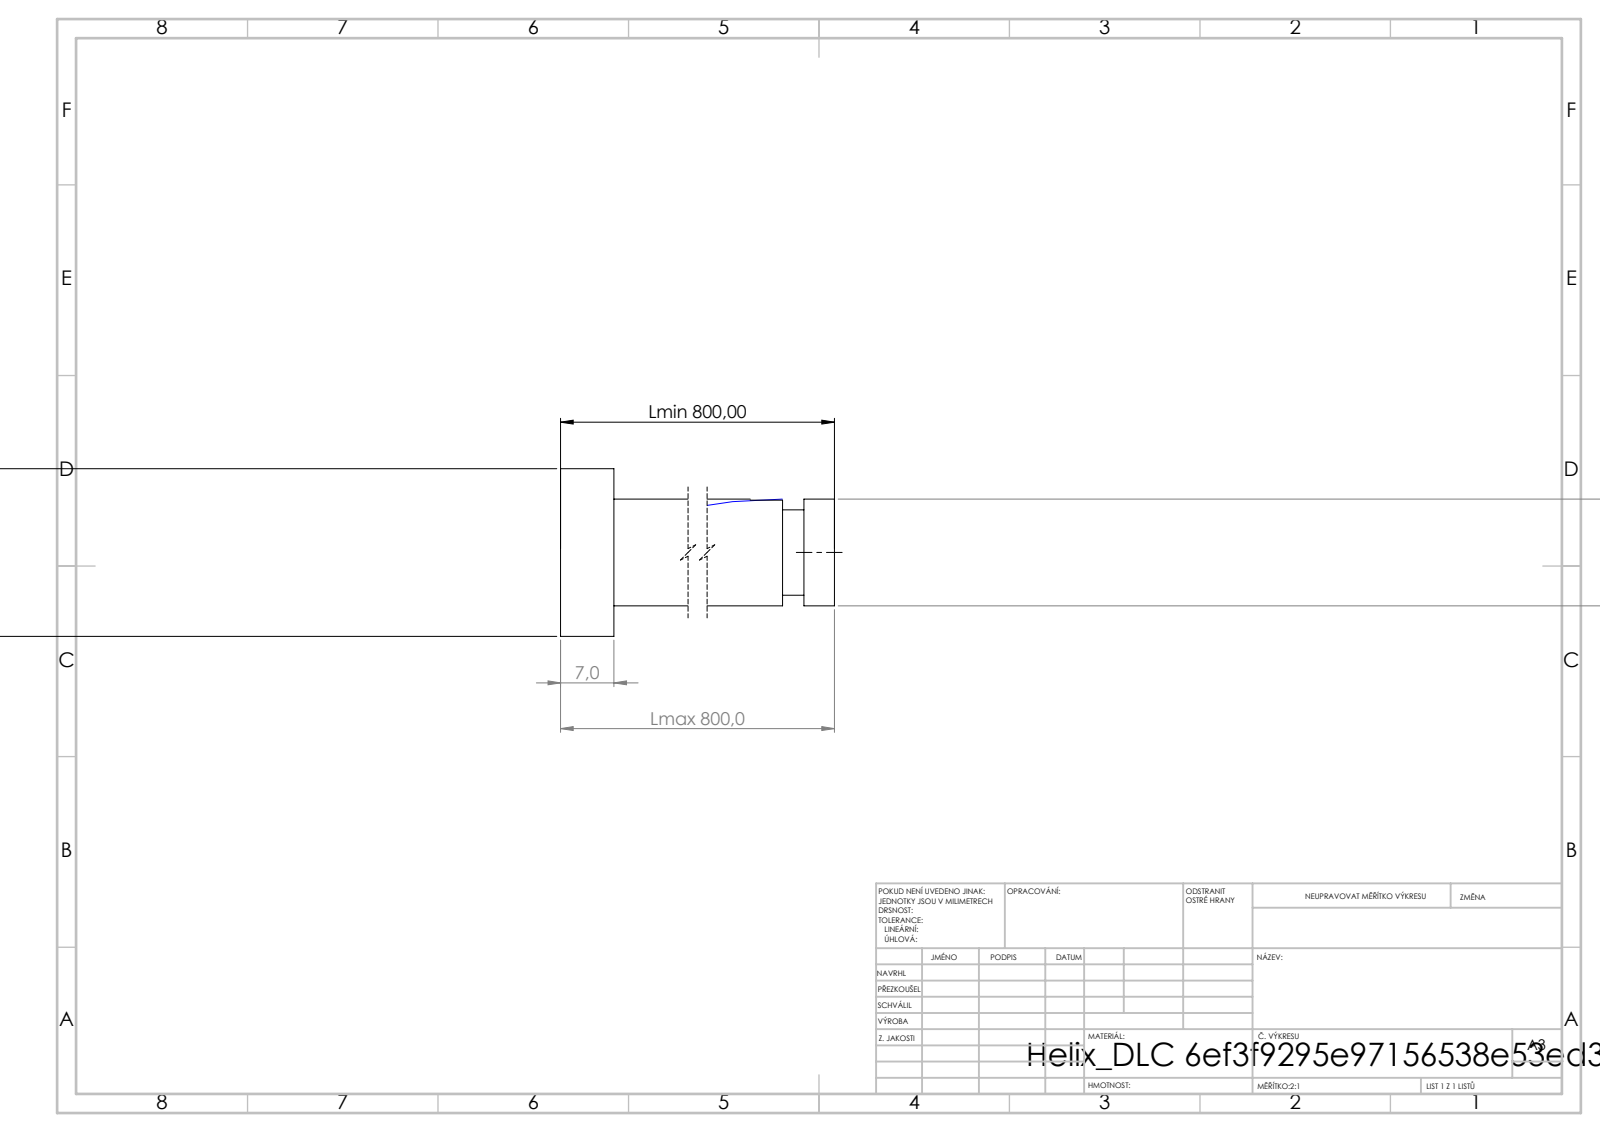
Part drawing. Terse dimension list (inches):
written by: SolidWorks 2019 (CONFIG_CONTROL_DESIGN)
unit: in
bodies: 1 solid, 16 faces (6 planar, 9 cylindrical, 1 other)
size: 31.496 × 0.866 × 0.866
volume: 9.2 in³; area: 75.18 in²
bosses: 1× ⌀0.866, 1× ⌀0.551, 1× ⌀0.441
face distances: 0.276, 31.496, 31.22, 31.338, 31.063, 0.158, 31.228, 30.952, 0.11, 0.268
